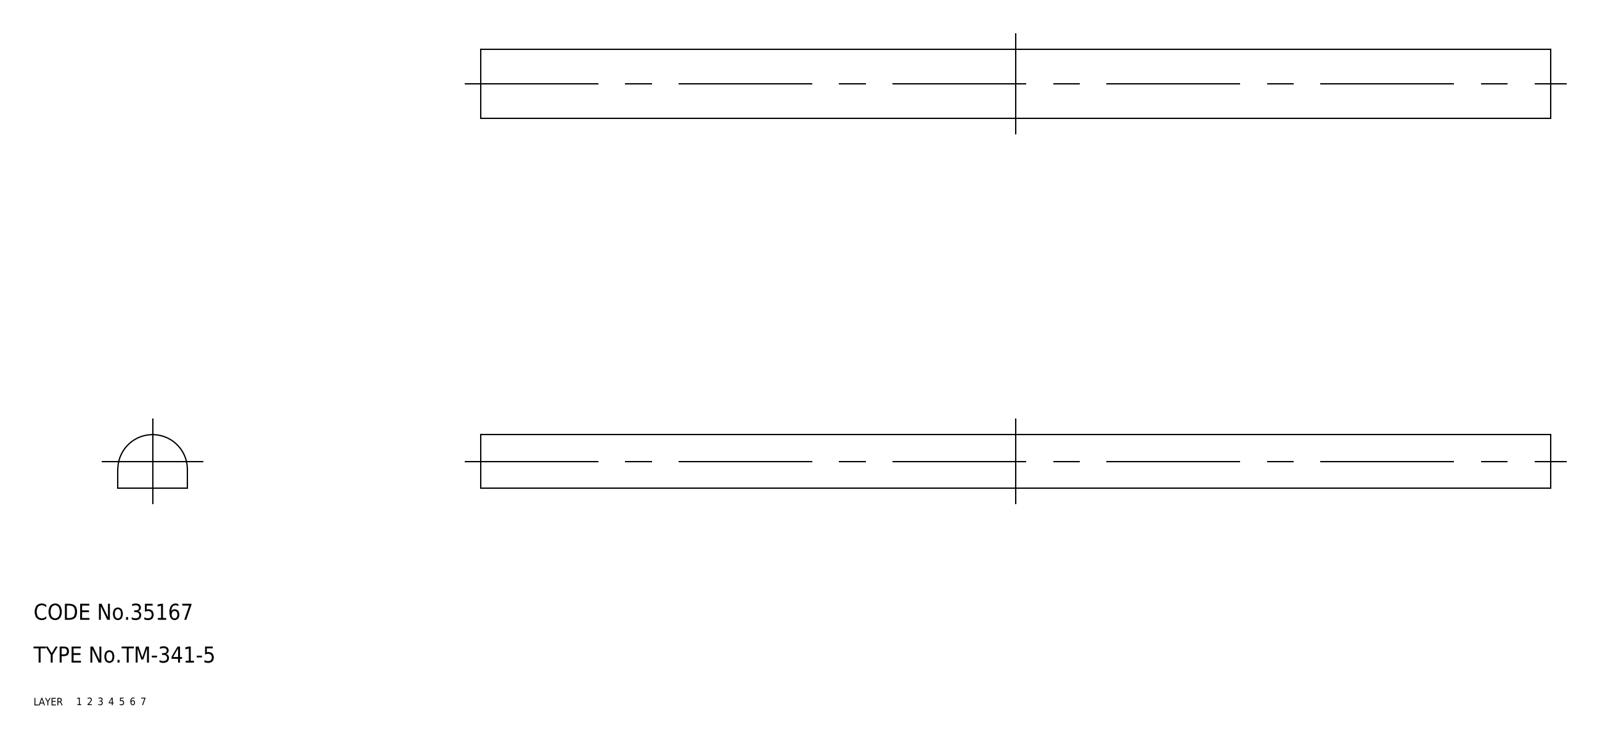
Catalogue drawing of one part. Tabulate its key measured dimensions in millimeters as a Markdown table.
| quantity | value |
| --- | --- |
| part name | TM_341_5; rubber foam |
| STEP written by | SolidWorks 2015 (AUTOMOTIVE_DESIGN) |
| units | millimeters |
| bodies | 1 solid, 6 faces (5 planar, 1 cylindrical, 0 other) |
| overall size | 200 × 13 × 10 |
| volume | 22 373 mm³ |
| surface area | 8 308 mm² |
| partial cylindrical surfaces (radius × count) | 6.5 × 1 |
| main face-to-face distances | 13, 200 |
